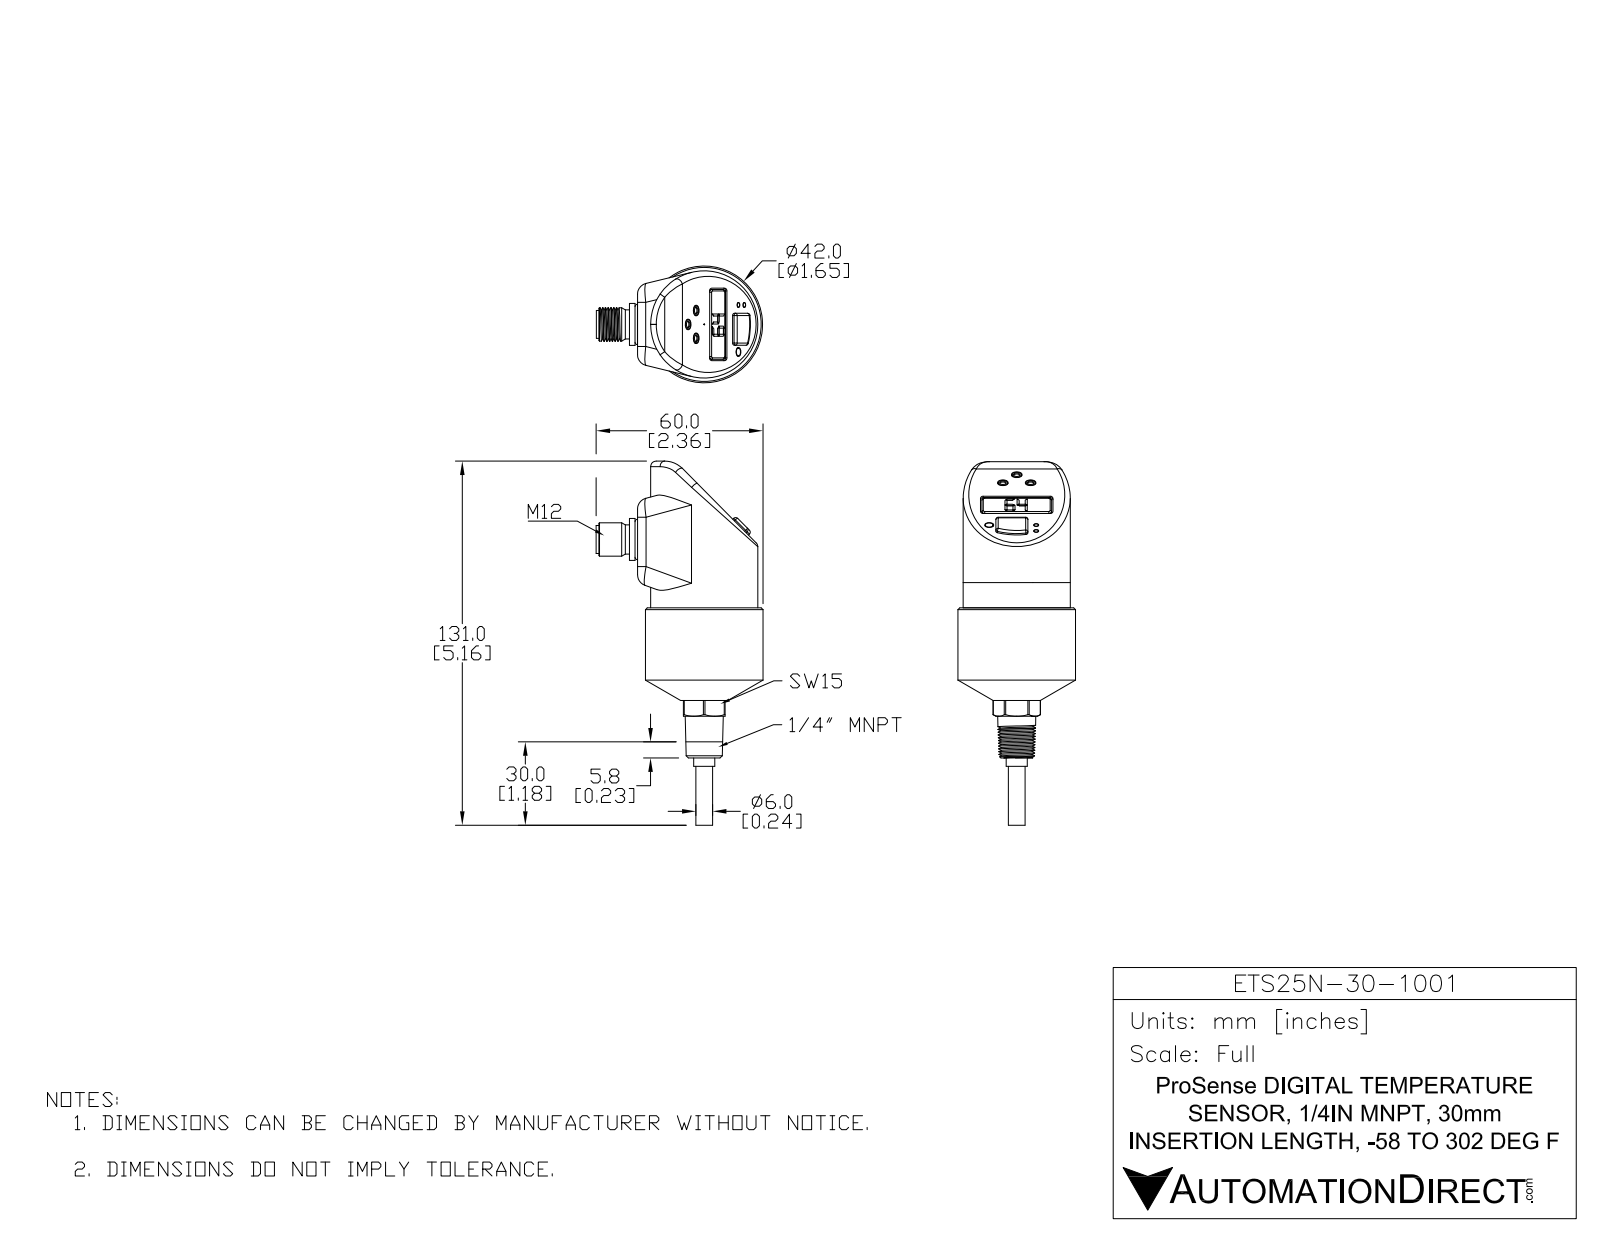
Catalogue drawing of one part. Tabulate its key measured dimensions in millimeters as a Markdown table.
| quantity | value |
| --- | --- |
| part name | ETS25N-30-1001 |
| STEP written by | SolidWorks 2016 (AUTOMOTIVE_DESIGN) |
| units | millimeters |
| bodies | 2 solids, 323 faces (138 planar, 95 cylindrical, 90 other) |
| overall size | 130.8 × 59.95 × 42.3 |
| volume | 101 659 mm³ |
| surface area | 18 058 mm² |
| round holes (diameter × count) | 8.45 × 1 |
| round bosses / shafts (diameter × count) | 1.4 × 4, 1 × 4, 42.3 × 1, 38.55 × 1, 15.1 × 1, 14.56 × 1, 12 × 1, 11 × 1 |
| partial cylindrical surfaces (radius × count) | 1 × 8, 0.8 × 7, 0.5 × 4, 3.99 × 4, 7 × 4, 0.61 × 1, 2 × 1, 8.5 × 1 |
| main face-to-face distances | 15, 0.9, 2, 2.9, 1.5, 54, 13.9, 4, 1.1, 3.1 |
